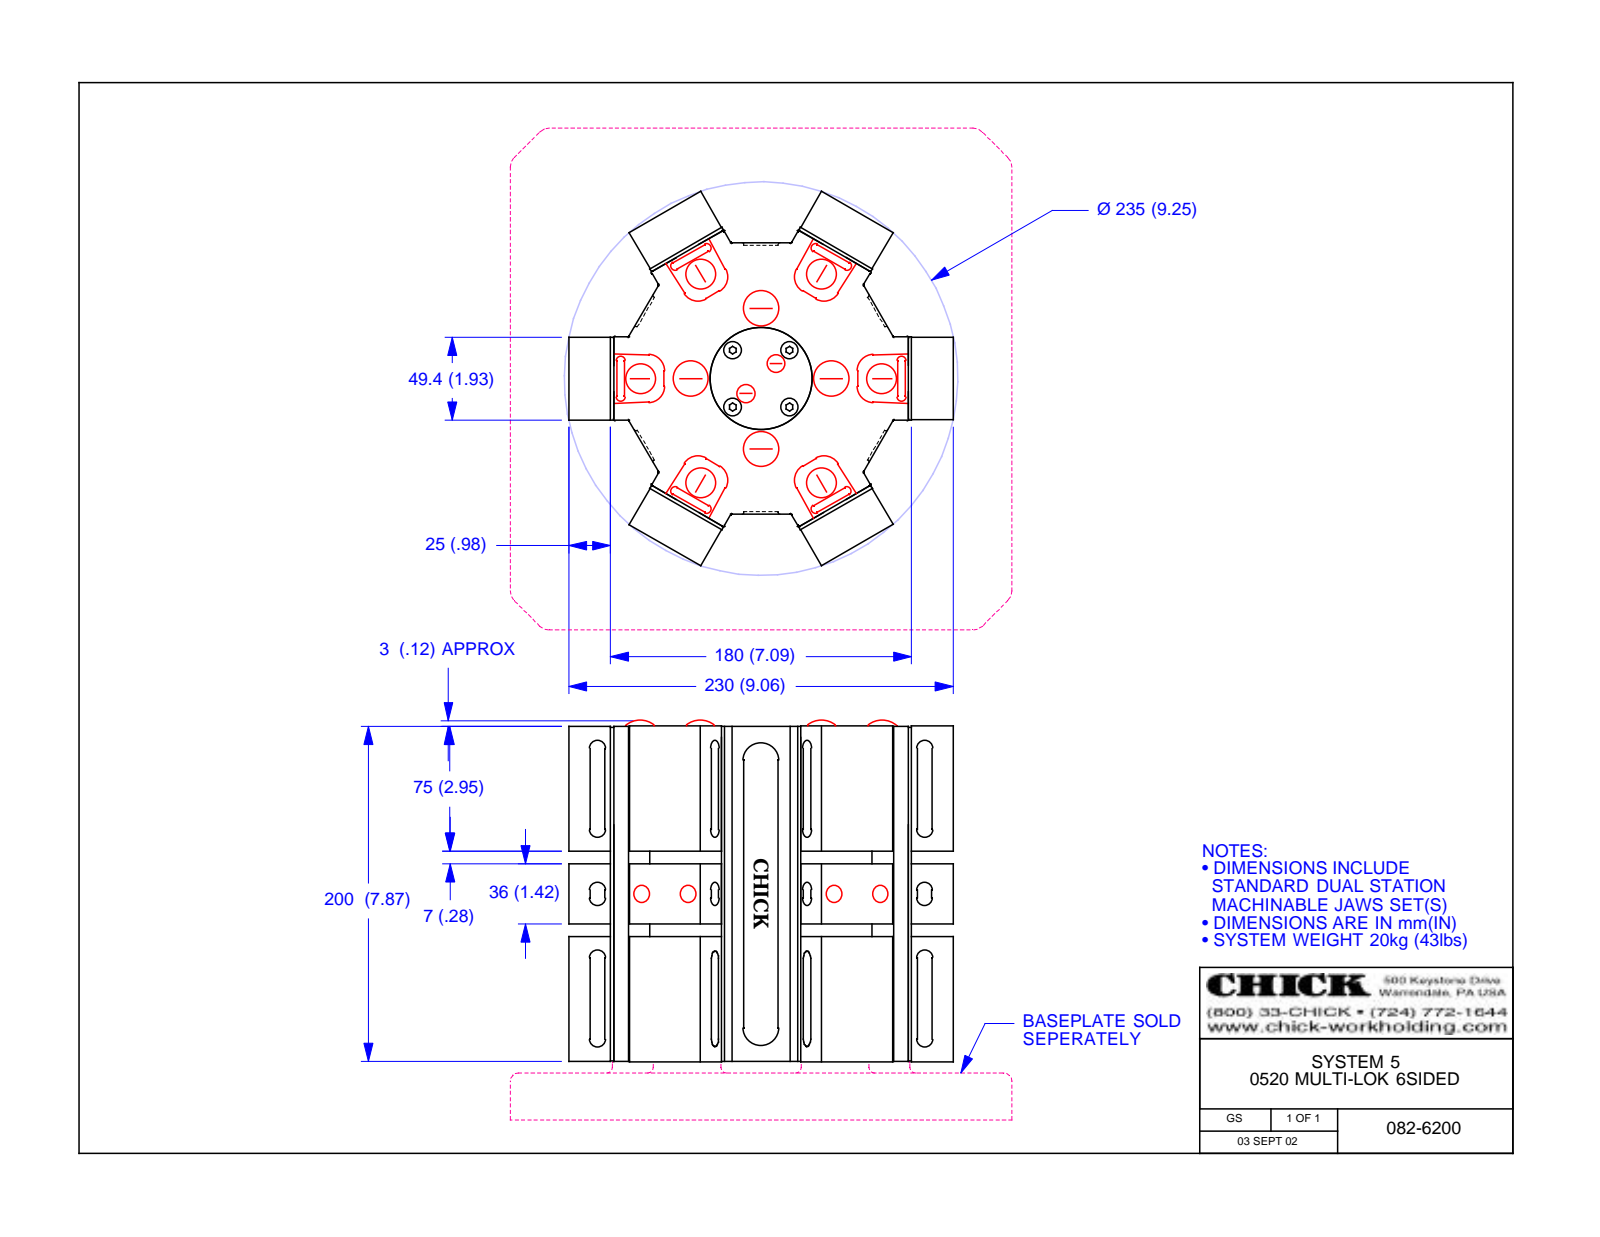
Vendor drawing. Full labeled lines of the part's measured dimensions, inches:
Part name (STEP PRODUCT): 082-6200; 082-6210; 080-0313-21; 080-2500 (+2 more)
STEP written by: Autodesk Inventor 2013 (AUTOMOTIVE_DESIGN)
Units: inches
Bodies: 25 solids, 2944 faces (1173 planar, 682 cylindrical, 1089 other)
Overall size (bounding box): 9.055 × 8.791 × 8.031
Volume: 315.1 in³ · Surface area: 1 021 in²
Round holes (diameter × count): ⌀0.5 ×30, ⌀0.163 ×18, ⌀0.394 ×18, ⌀0.205 ×10, ⌀0.38 ×10, ⌀0.787 ×7, ⌀0.36 ×6, ⌀0.398 ×6, ⌀0.531 ×5, ⌀0.728 ×4, ⌀0.541 ×3, ⌀0.712 ×2
Round bosses / shafts (diameter × count): ⌀0.551 ×18, ⌀0.604 ×3, ⌀0.375 ×3
Partial cylindrical surfaces — rounded edges, fillets, slot ends (radius × count): R0.031 ×192, R0.039 ×36, R0.094 ×20, R0.075 ×12, R0.311 ×12, R0.437 ×12, R0.13 ×6, R0.223 ×6
Main face-to-face distances: 0.079, 7.008, 1.063, 0.984, 7.992, 8.071, 6.929, 2.913, 3.465, 7.087
Hole centre spacings: 2.953, 3.21, 1.26, 5.906, 6.039, 1.26, 2.461, 6.038
